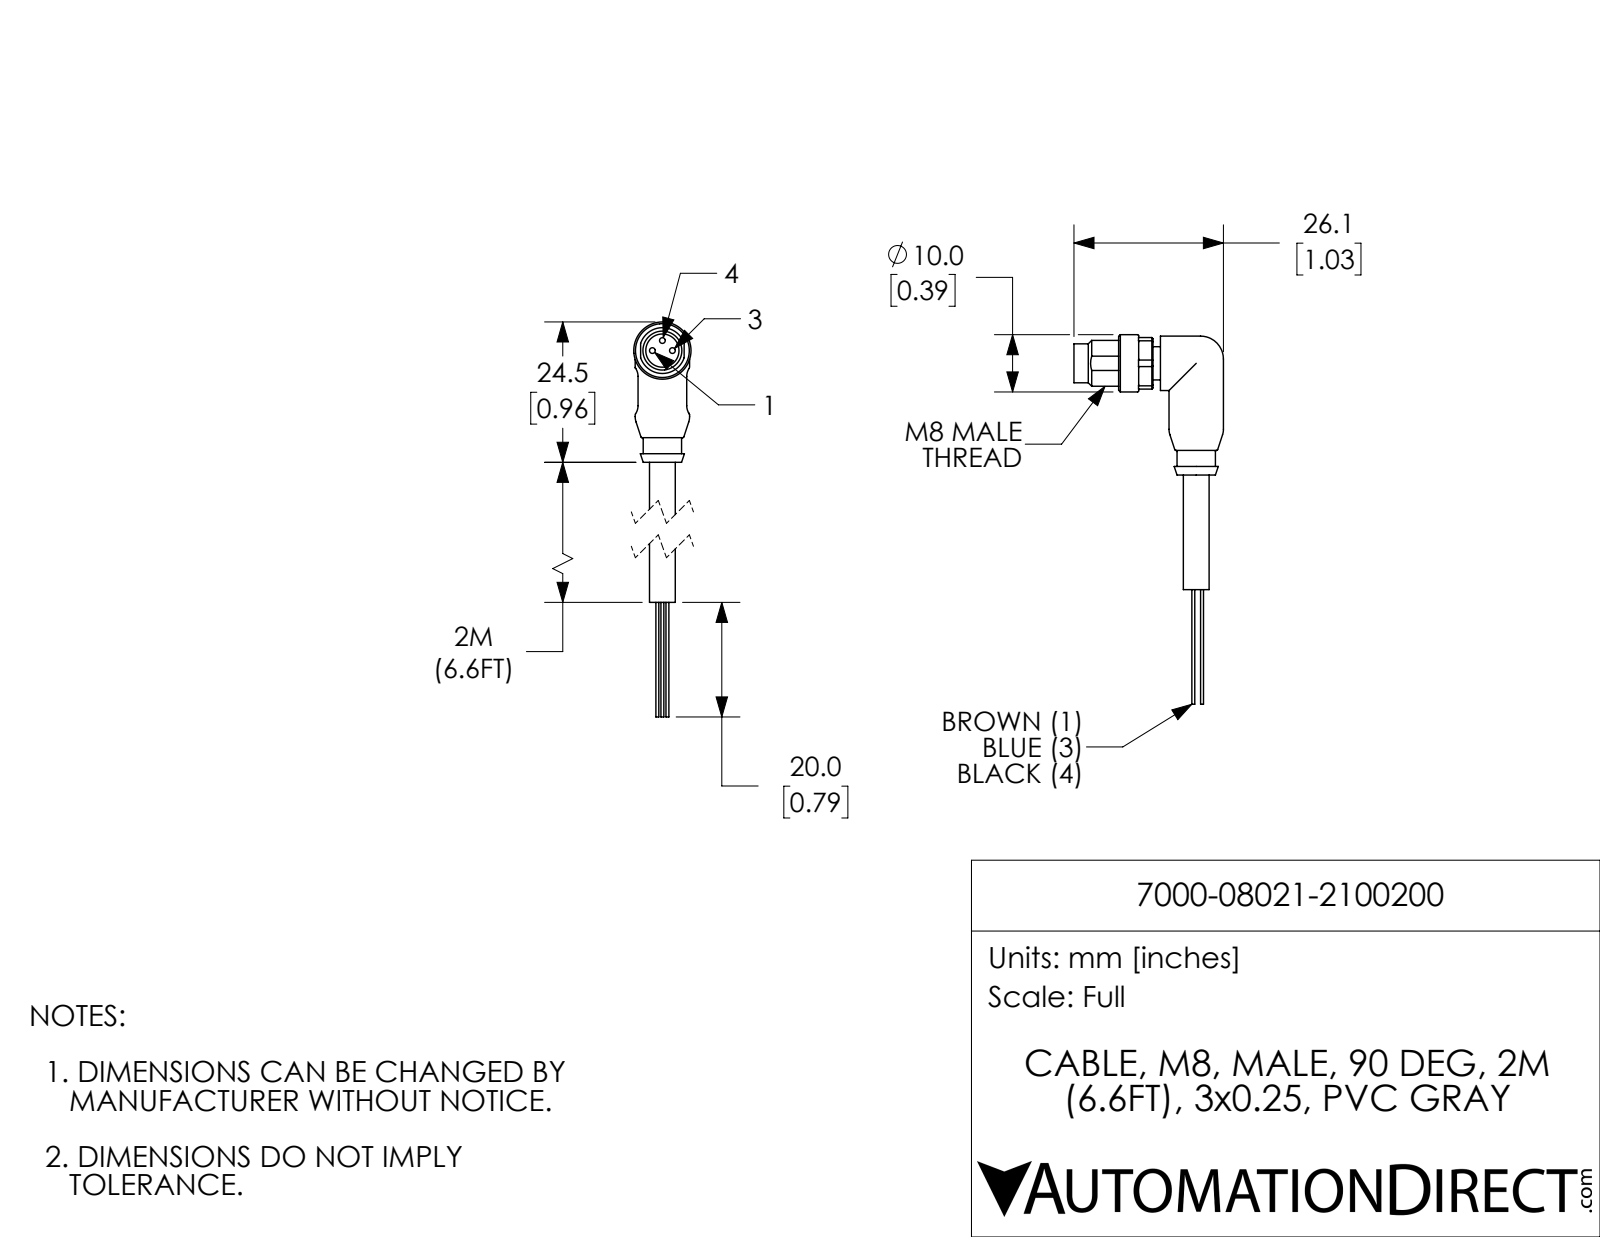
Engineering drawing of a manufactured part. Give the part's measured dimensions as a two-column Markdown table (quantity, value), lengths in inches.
| quantity | value |
| --- | --- |
| part name | 7000-08021-2100200 |
| STEP written by | SolidWorks 2017 (AUTOMOTIVE_DESIGN) |
| units | inches |
| bodies | 4 solids, 118 faces (40 planar, 45 cylindrical, 33 other) |
| overall size | 2.539 × 1.028 × 0.394 |
| volume | 0.161 in³ |
| surface area | 2.831 in² |
| round holes (diameter × count) | 0.228 × 1 |
| round bosses / shafts (diameter × count) | 0.039 × 3, 0.02 × 3, 0.374 × 2, 0.394 × 1, 0.315 × 1, 0.268 × 1, 0.264 × 1, 0.177 × 1 |
| partial cylindrical surfaces (radius × count) | 0.008 × 4, 0.098 × 4, 0.193 × 1 |
| main face-to-face distances | 0.051, 0.354, 0.018, 0.317, 0.346, 0.398, 0.335, 0.11, 0.236, 0.287 |
